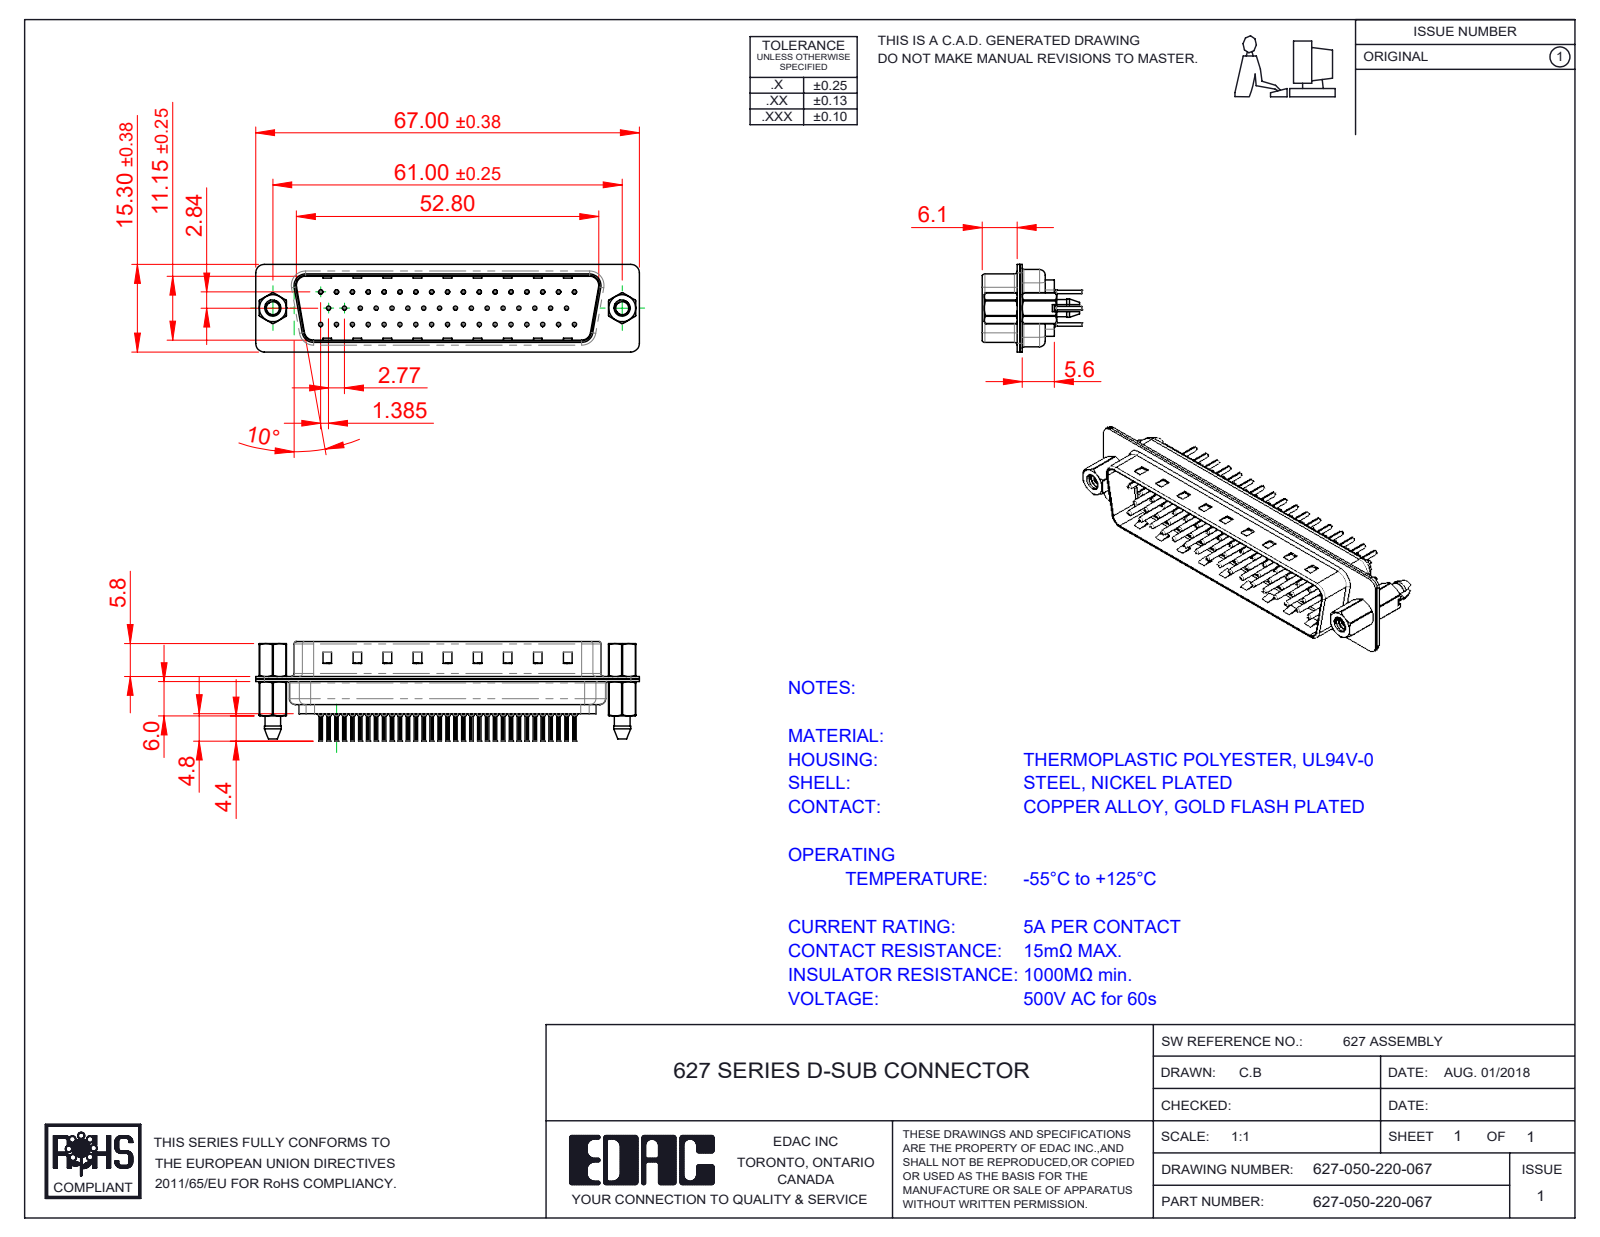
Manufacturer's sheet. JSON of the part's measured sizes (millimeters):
{"part_name": "627 Shell Rear_50 Contacts; 627 4-40 Hex Standoff; 627 Contact Row 2_20L; 627-050-220-067 (+5 more)", "step_written_by": "SolidWorks 2020 (CONFIG_CONTROL_DESIGN)", "units": "millimeters", "bodies": {"solids": 57, "faces": 5512, "planar": 1457, "cylindrical": 2095, "other": 1960}, "overall_size": [67, 17.3, 15.3], "volume_mm3": 4751, "surface_area_mm2": 13358, "round_holes": [[0.2, 50], [0.35, 50], [1.1, 50], [1.6, 50], [2.26, 2], [2.29, 2], [4, 2], [4.8, 2]], "round_bosses_or_shafts": [[2, 50], [1.5, 50], [0.75, 50], [0.6, 50], [4.9, 2], [2.79, 2]], "partial_cylinders_radius": [[0.1, 100], [1.5, 18], [2, 12], [1.6, 10], [0.5, 8], [0.25, 4], [0.6, 4], [0.65, 4]], "face_to_face_distances": [0.4, 0.45, 11.55, 0.9, 6.05, 6.5, 0.78, 12.33, 1.95, 0.77], "hole_center_spacings": [3.16, 2.77, 5.54, 8.31, 11.08, 13.85, 16.62, 5.03]}
